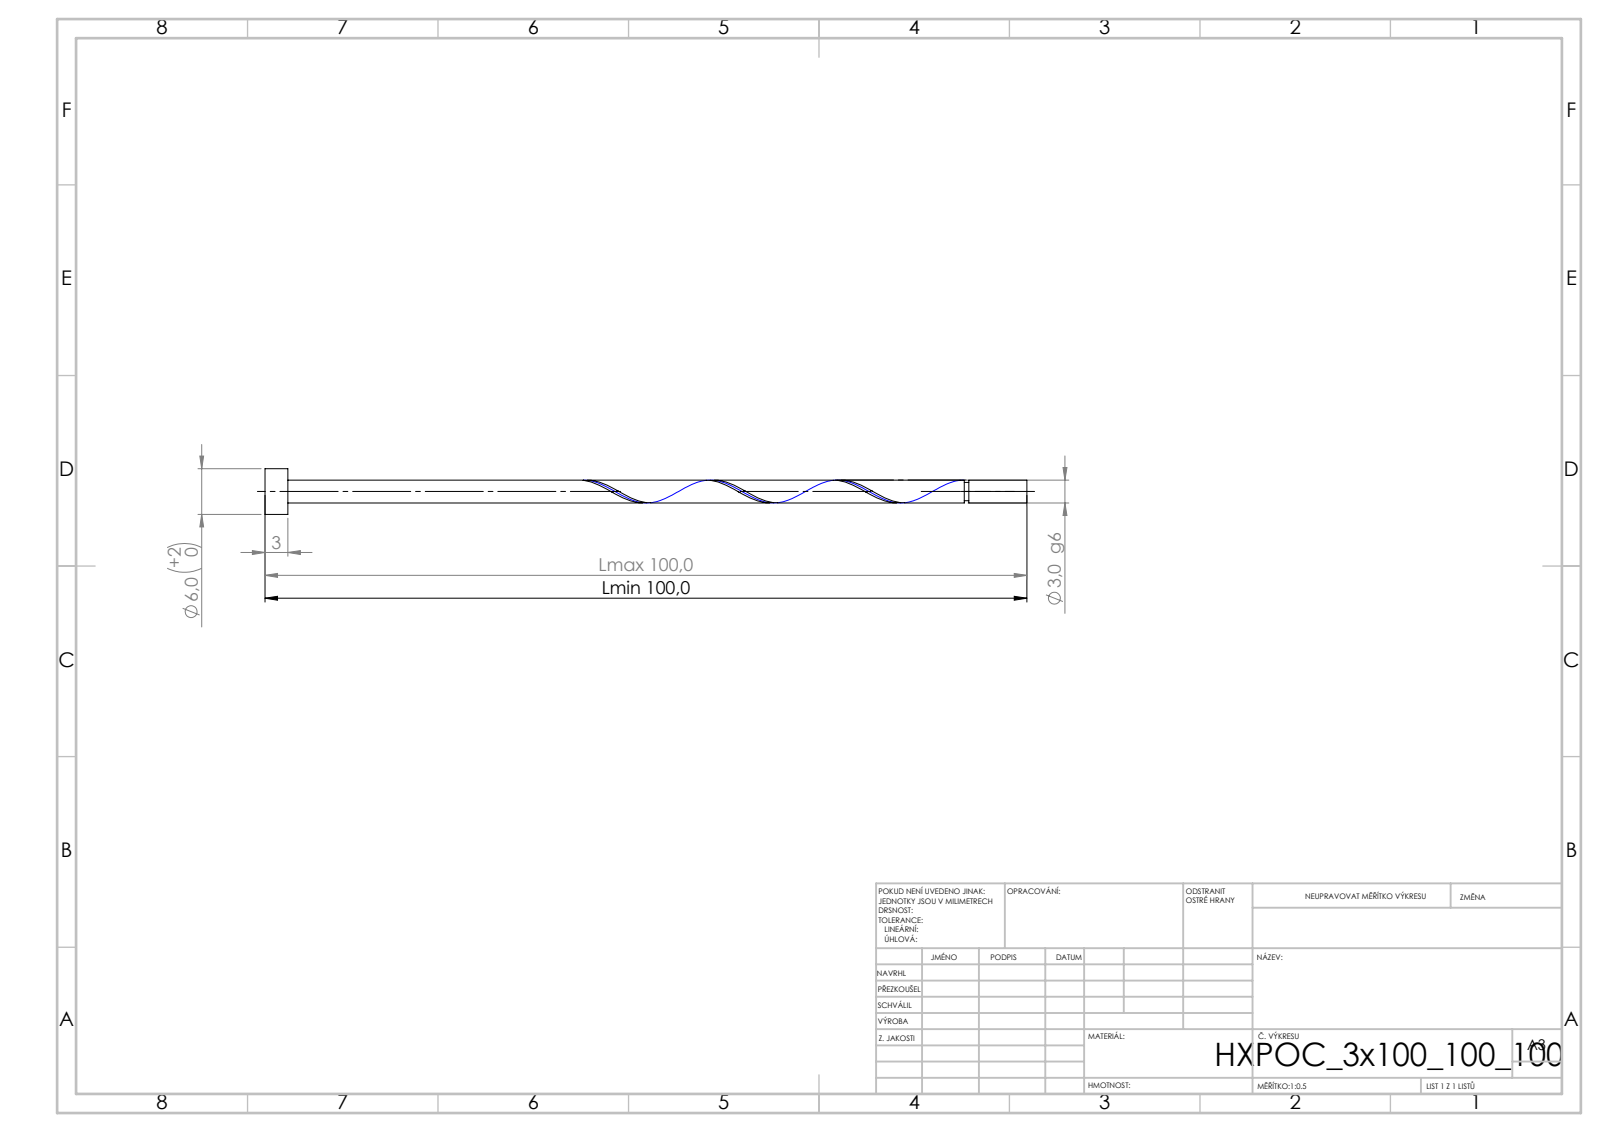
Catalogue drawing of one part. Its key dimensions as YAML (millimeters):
step_written_by: "SolidWorks 2019 (CONFIG_CONTROL_DESIGN)"
units: millimeters
bodies: {solids: 1, faces: 21, planar: 6, cylindrical: 14, other: 1}
overall_size: [100, 6, 6]
volume: 762
surface_area: 1048
round_bosses_or_shafts:
  - {diameter: 6, count: 1}
  - {diameter: 3, count: 1}
  - {diameter: 2.4, count: 1}
face_to_face_distances: [3, 100, 97, 92.37, 89.37, 7.63, 91.77, 88.77, 0.6, 8.23]
